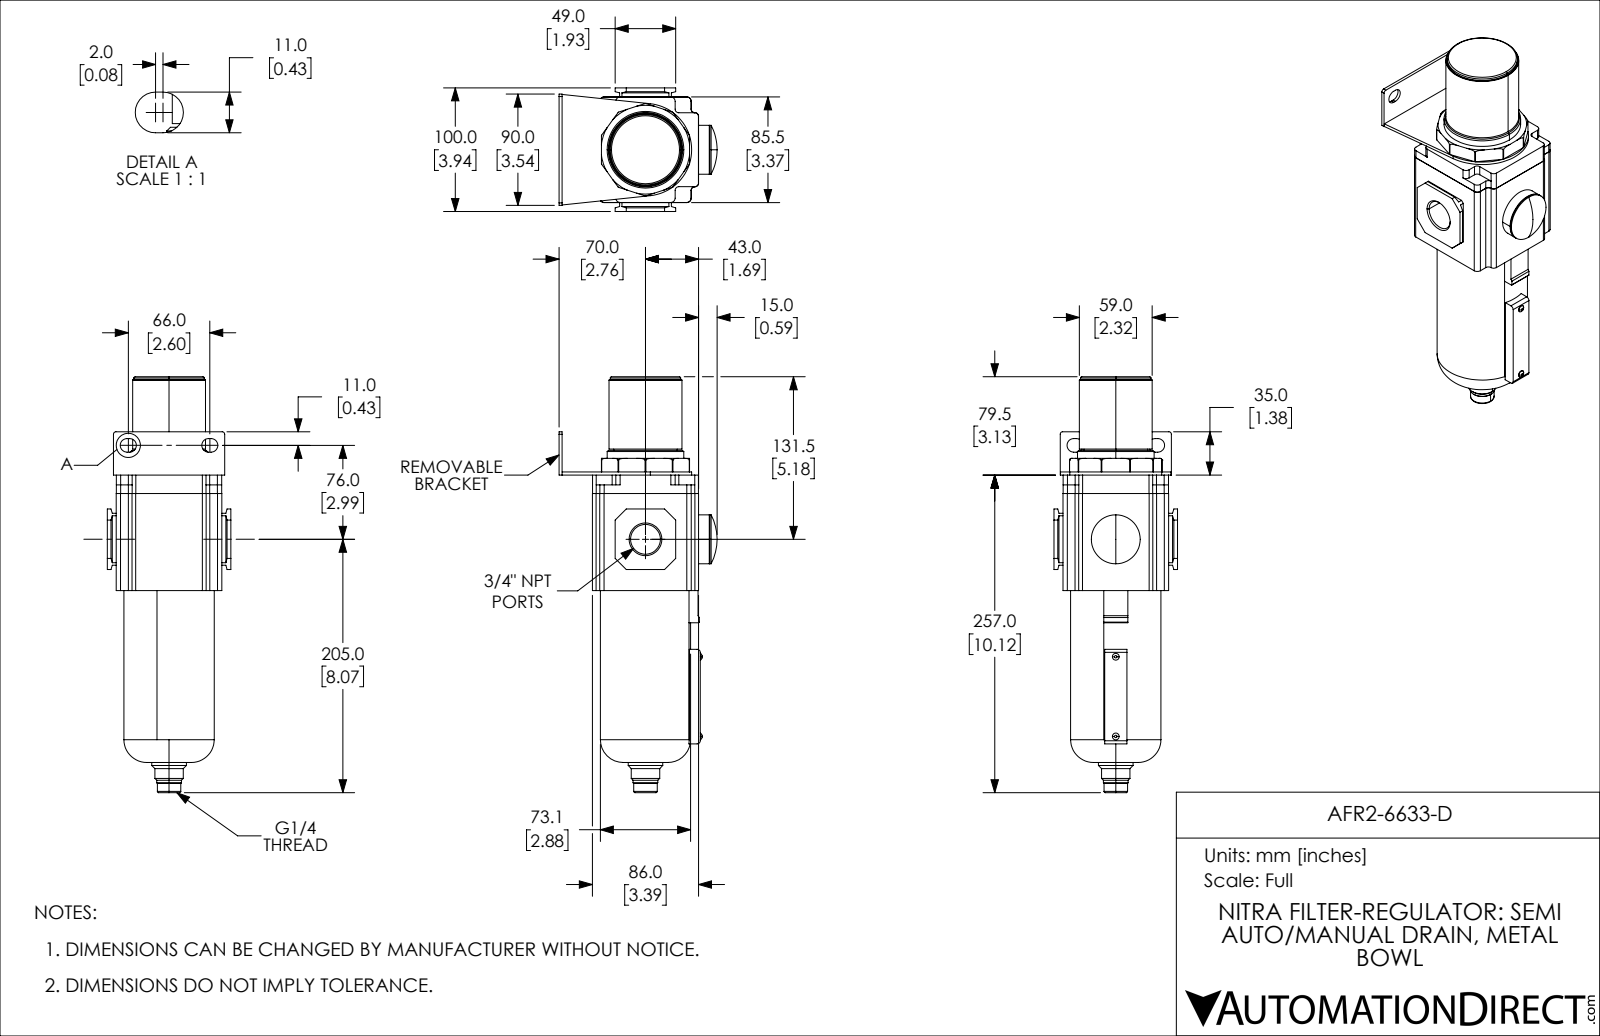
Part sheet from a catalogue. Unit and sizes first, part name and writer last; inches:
Units: inches
Overall size (bounding box): 13.248 × 5.039 × 3.937
Round holes (diameter × count): ⌀0.451 ×1, ⌀0.95 ×1
Round bosses / shafts (diameter × count): ⌀0.217 ×2, ⌀2.878 ×1, ⌀2.441 ×1, ⌀2.323 ×1, ⌀2.244 ×1, ⌀2.024 ×1, ⌀1.559 ×1, ⌀1.102 ×1
Partial cylindrical surfaces — rounded edges, fillets, slot ends (radius × count): R0.118 ×20, R0.138 ×12, R0.217 ×4, R0.079 ×2, R0.098 ×2, R1.472 ×1
Main face-to-face distances: 0.098, 3.366, 0.285, 3.652, 3.386, 4.35, 1.063, 4.449, 3.681, 3.78
Volume: 92.63 in³ · Surface area: 179.5 in²
Bodies: 1 solid, 235 faces (116 planar, 79 cylindrical, 40 other)
Part name (STEP PRODUCT): AFR2-6633-D
STEP written by: SolidWorks 2019 (CONFIG_CONTROL_DESIGN)
